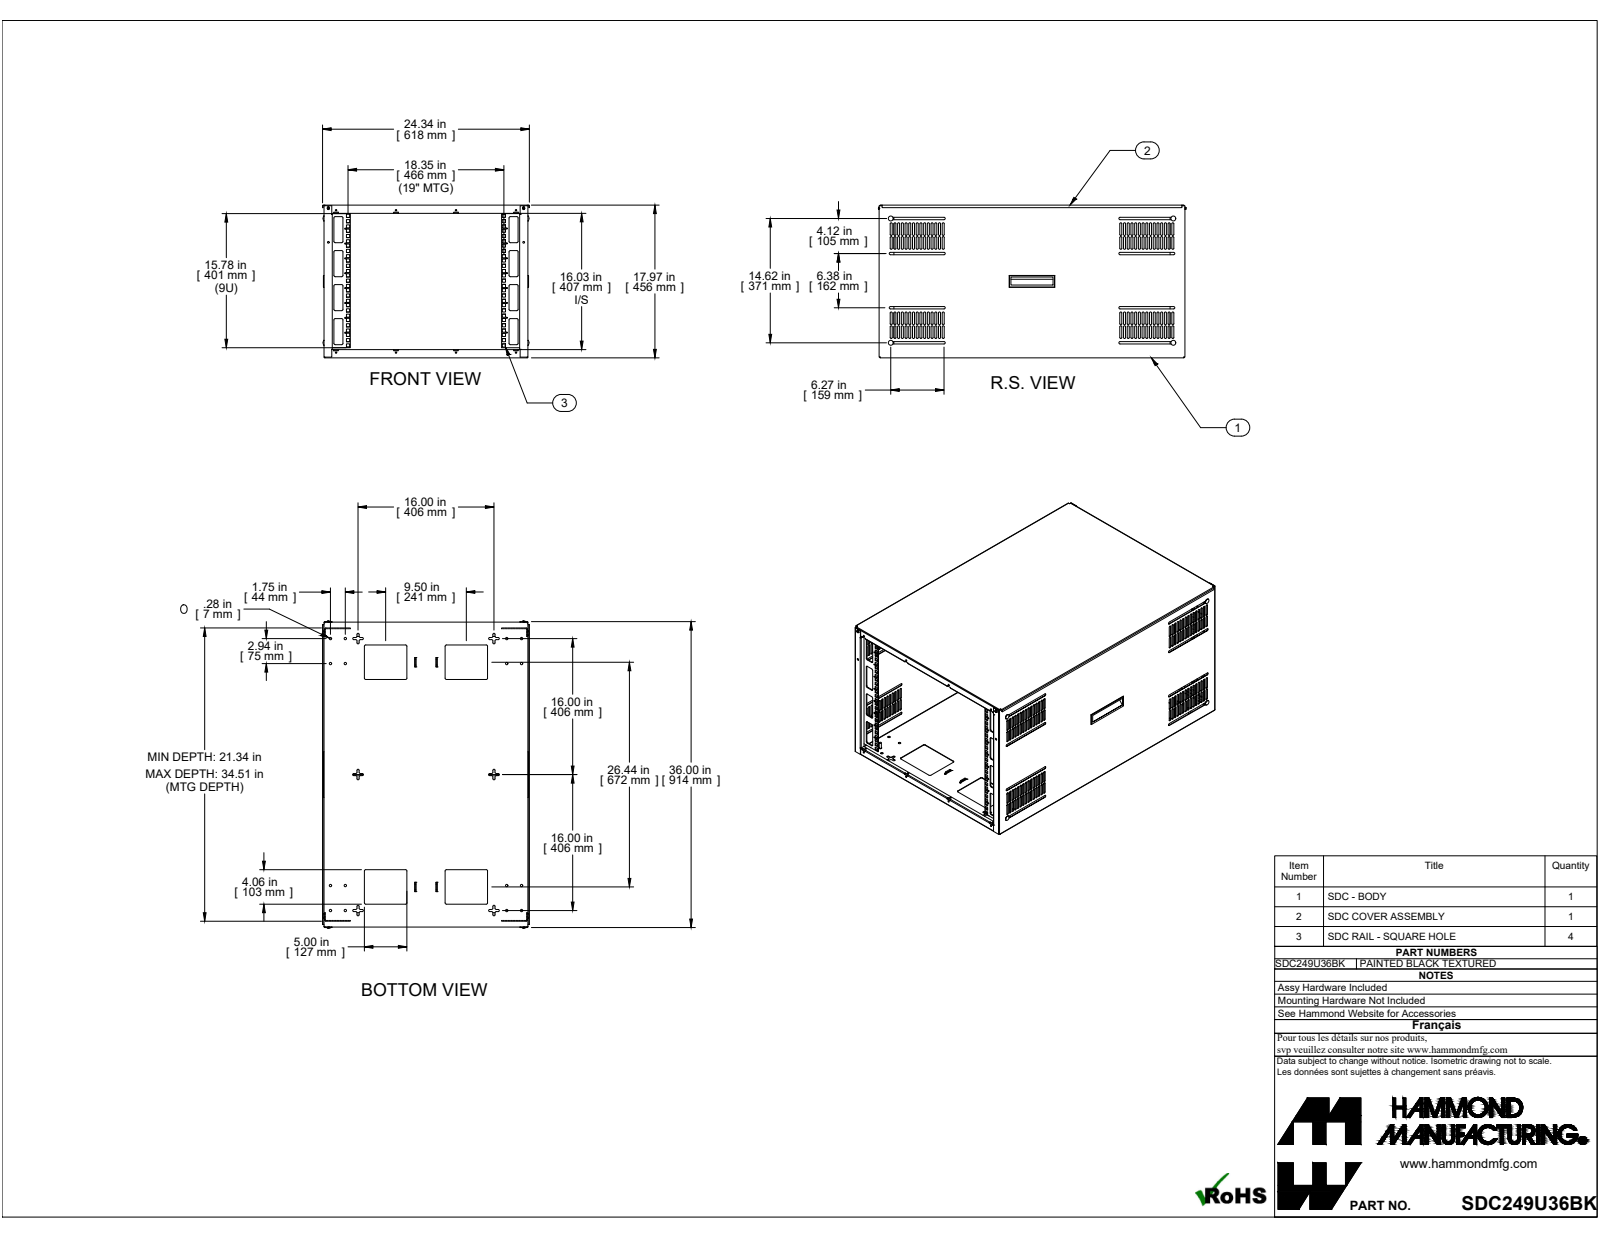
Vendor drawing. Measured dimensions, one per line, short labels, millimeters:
name: SDC249U36BK
written by: SolidWorks 2019 (CONFIG_CONTROL_DESIGN)
unit: mm
bodies: 37 solids, 2852 faces (1814 planar, 986 cylindrical, 52 other)
size: 918.7 × 618.3 × 456.5
volume: 3 302 000 mm³; area: 4 435 000 mm²
holes: 32× ⌀3.2, 16× ⌀4.3, 16× ⌀7.1, 4× ⌀5, 2× ⌀4, 2× ⌀4.7, 2× ⌀5.4
bosses: 8× ⌀6.4, 4× ⌀14.7, 2× ⌀8, 2× ⌀7.1, 2× ⌀4.7, 2× ⌀3.5
rounds: 240× R3, 76× R4, 24× R3.2, 22× R0.7, 22× R2.2, 16× R0.6, 16× R3, 16× R3.6
face distances: 1.4, 455, 608.2, 453.6, 456.5, 606.7, 609.6, 1.8, 23.2, 2.4
hole spacings: 44.5, 484.8, 88.9, 133.4, 482.7, 74.6, 86.8, 177.8
